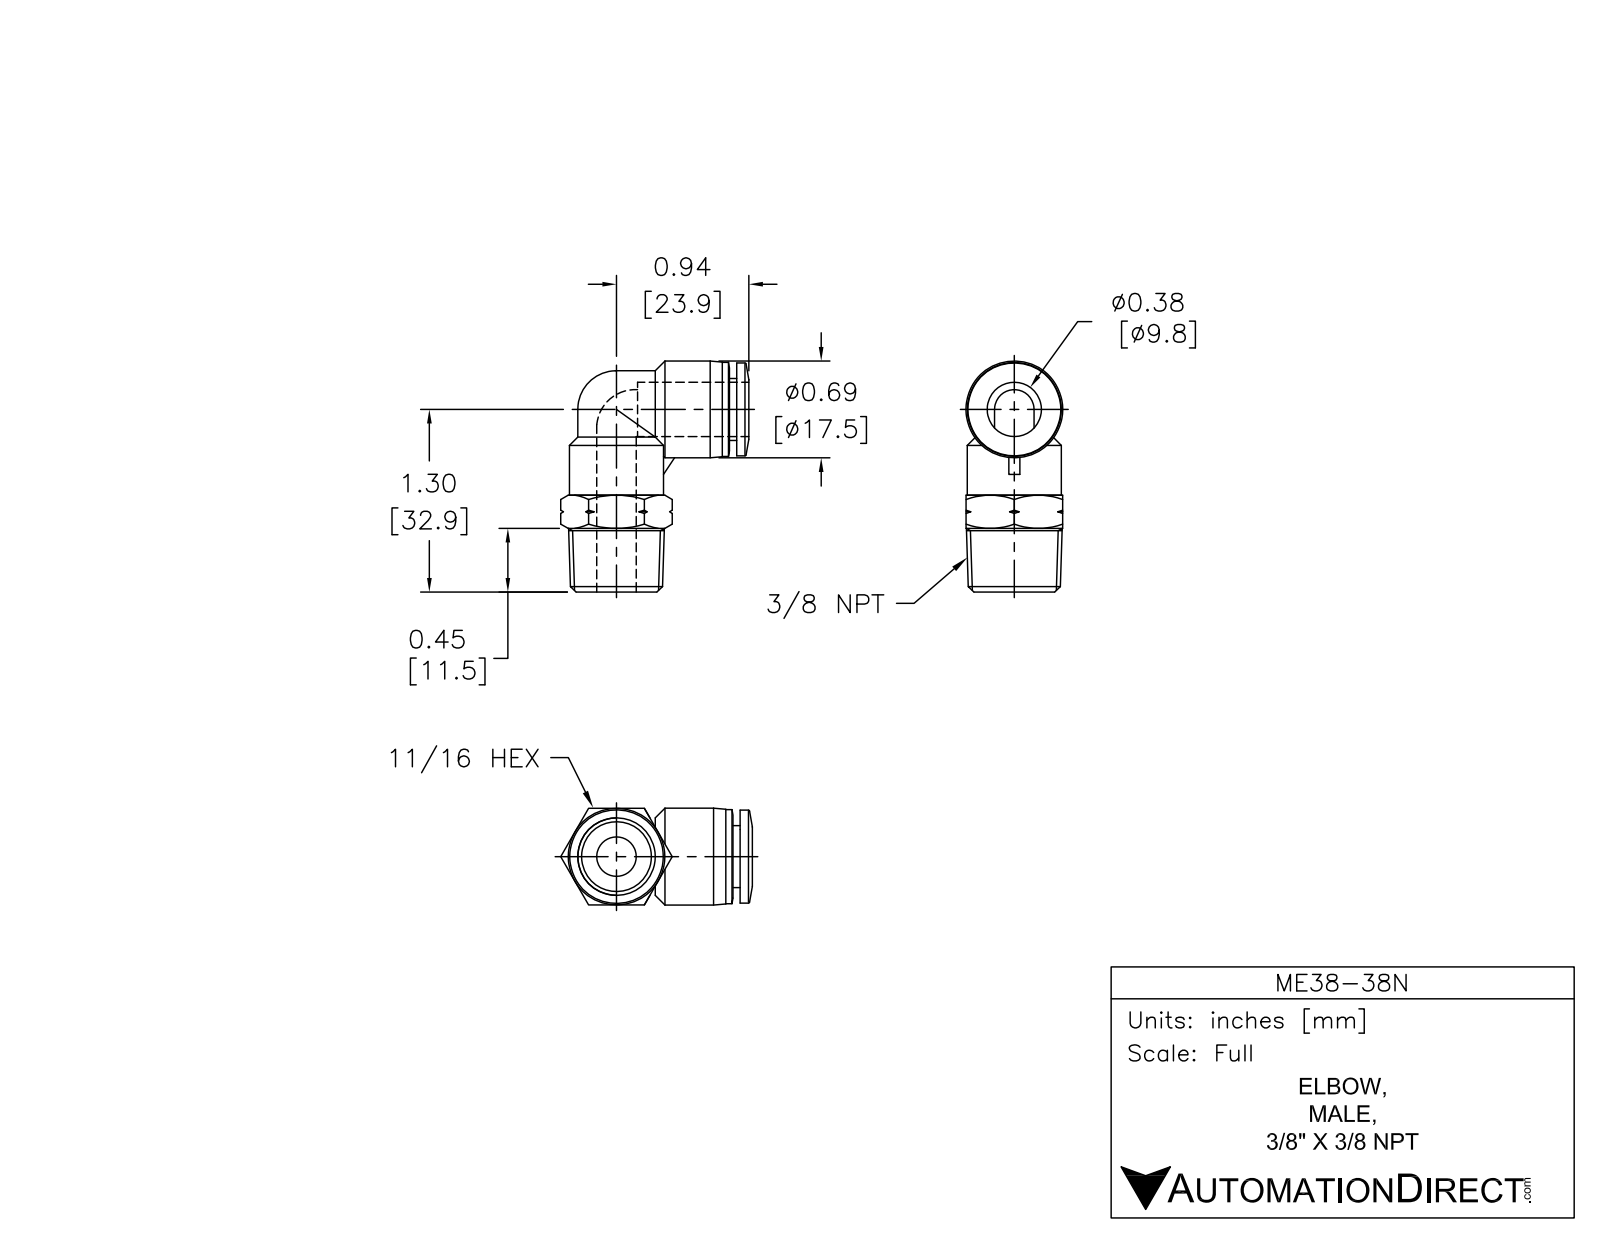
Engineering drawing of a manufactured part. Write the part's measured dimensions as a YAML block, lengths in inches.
part_name: "ME38-38N"
step_written_by: "SolidWorks 2015 (AUTOMOTIVE_DESIGN)"
units: inches
bodies: {solids: 1, faces: 87, planar: 16, cylindrical: 20, other: 51}
overall_size: [1.644, 1.363, 0.689]
volume: 0.556
surface_area: 7.734
round_holes:
  - {diameter: 0.276, count: 2}
  - {diameter: 0.386, count: 1}
round_bosses_or_shafts:
  - {diameter: 0.669, count: 2}
  - {diameter: 0.689, count: 1}
  - {diameter: 0.661, count: 1}
  - {diameter: 0.551, count: 1}
  - {diameter: 0.441, count: 1}
partial_cylinders:
  - {radius: 0.276, count: 1}
face_to_face_distances: [0.687, 0.051, 0.654, 0.705, 0.689, 0.304, 0.383, 0.079, 0.453, 0.236]
